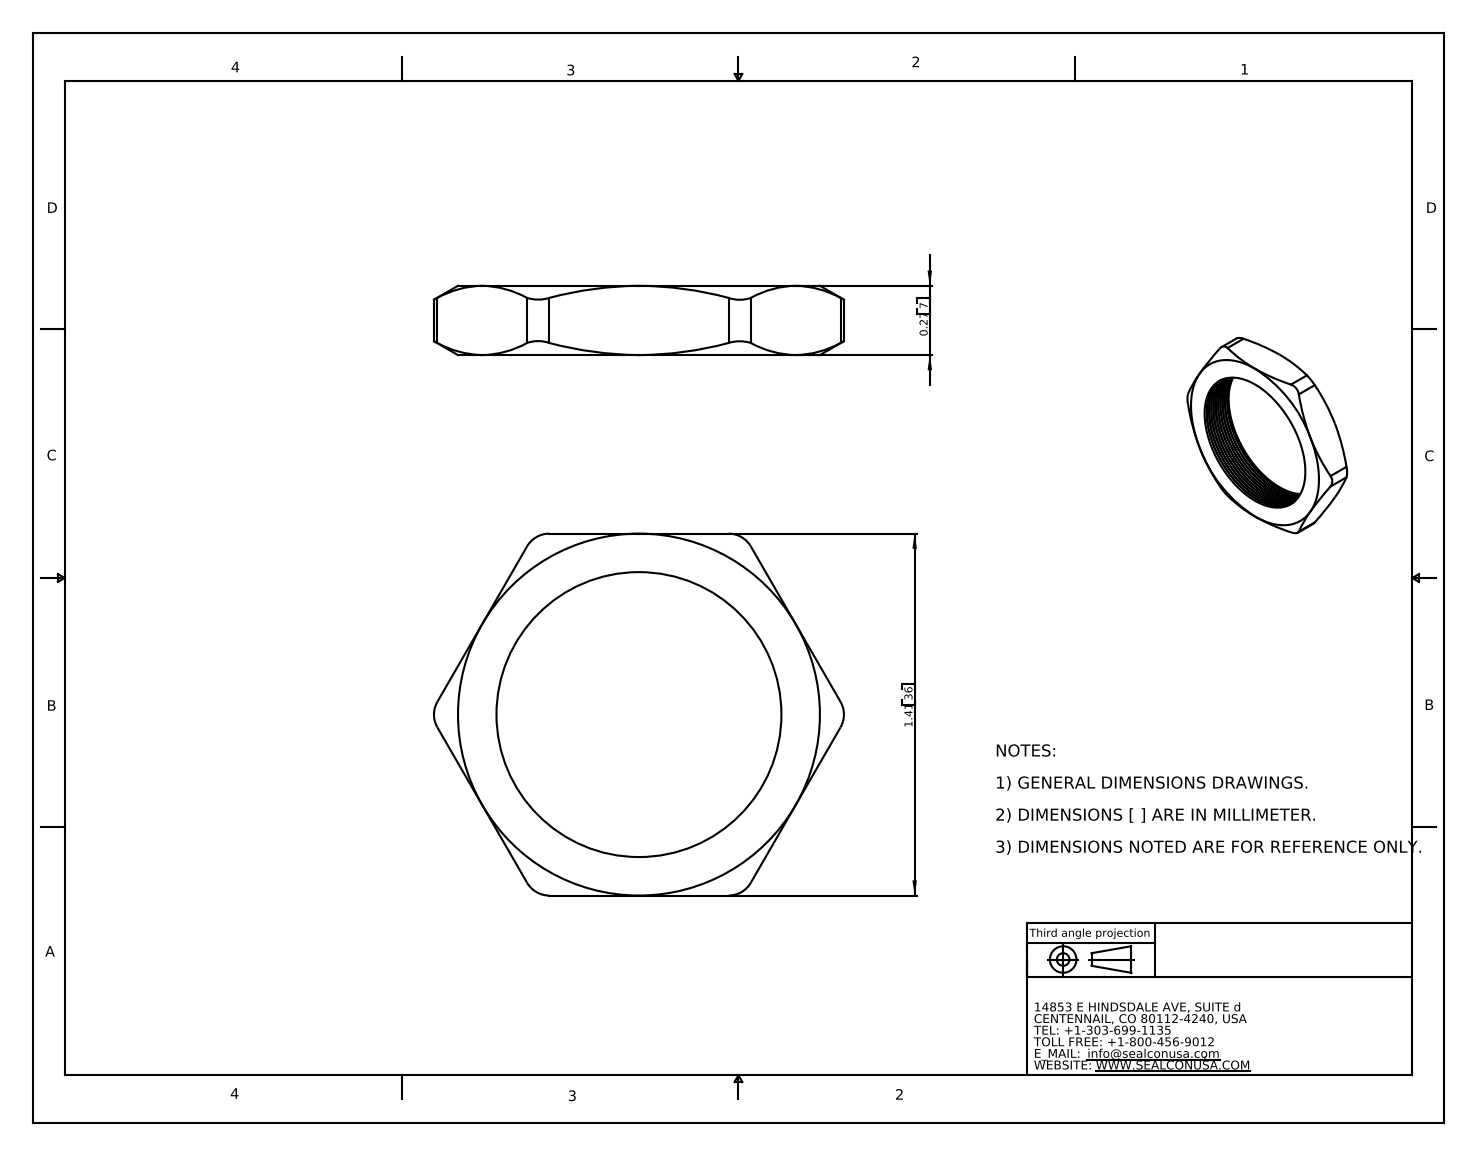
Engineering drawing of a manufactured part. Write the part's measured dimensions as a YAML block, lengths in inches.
part_name: "NP-21"
step_written_by: "SolidWorks 2007 (CONFIG_CONTROL_DESIGN)"
units: inches
bodies: {solids: 1, faces: 93, planar: 8, cylindrical: 27, other: 58}
overall_size: [1.597, 1.41, 0.27]
volume: 0.188
surface_area: 4.481
round_holes:
  - {diameter: 1.11, count: 1}
partial_cylinders:
  - {radius: 0.1, count: 6}
face_to_face_distances: [0.27, 1.41]
